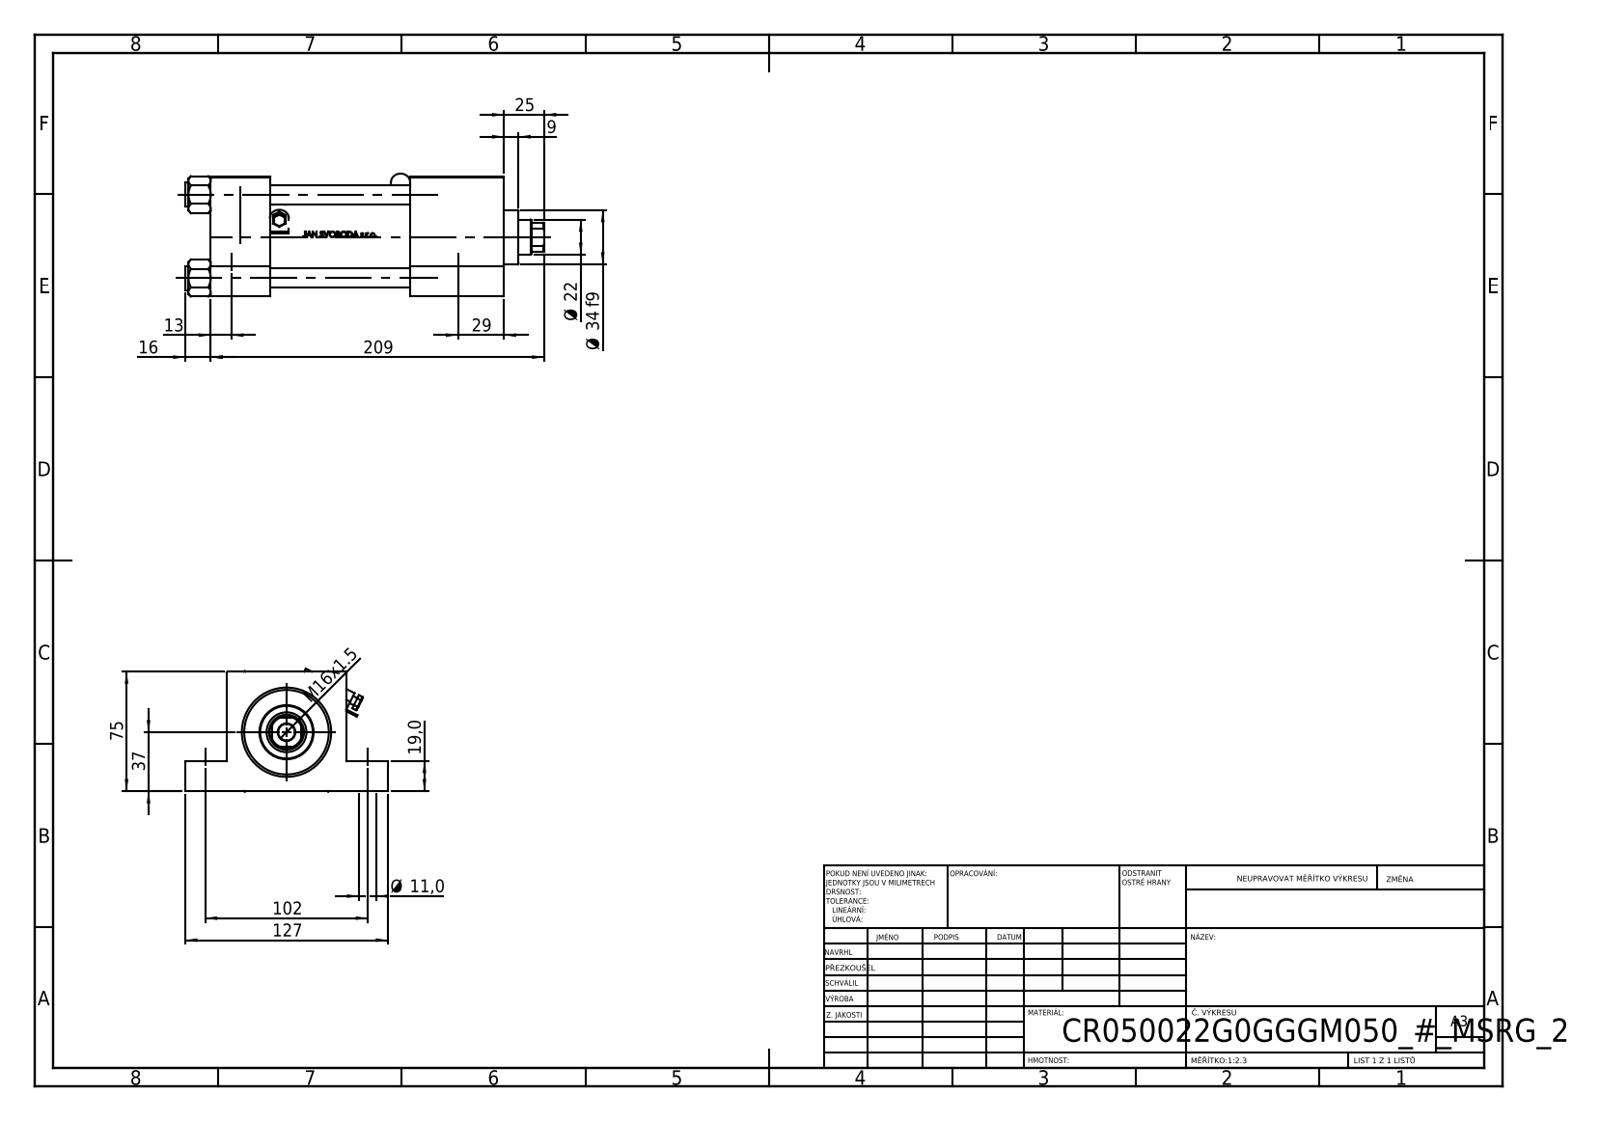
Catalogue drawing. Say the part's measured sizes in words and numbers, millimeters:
The part is named "V215_VC_A; V215CR_G_TYCINKA; V215CR_G_Body; NUT_M5_G (+2 more)". Its 3-D file was written by "SolidWorks 2019 (CONFIG_CONTROL_DESIGN)". It is 13 solids with 1152 faces: 468 planar, 152 cylindrical and 532 other. Overall it measures 225 by 127 by 77.15 millimeters. Its volume is 803 090 cubic millimeters and its surface area 180 446 square millimeters. Round holes: 4 of diameter 11, 4 of diameter 12, 2 of diameter 7, 2 of diameter 20.96, 2 of diameter 30, 1 of diameter 10.5, 1 of diameter 22, 1 of diameter 25, 1 of diameter 41, 1 of diameter 50, 1 of diameter 53. Round bosses or shafts: 4 of diameter 15, 2 of diameter 5, 2 of diameter 2.5, 1 of diameter 56, 1 of diameter 34. Partial cylindrical surfaces (rounded edges, fillets, slot ends): 12 of radius 0.5, 5 of radius 6, 1 of radius 10.5. The main face-to-face distances are 75, 37, 184, 147, 19, 56, 88, 101, 125, 59. The hole center spacings are 52.3, 36.63, 37.34, 51.3, 52.63, 73.96, 102, 138.72.
